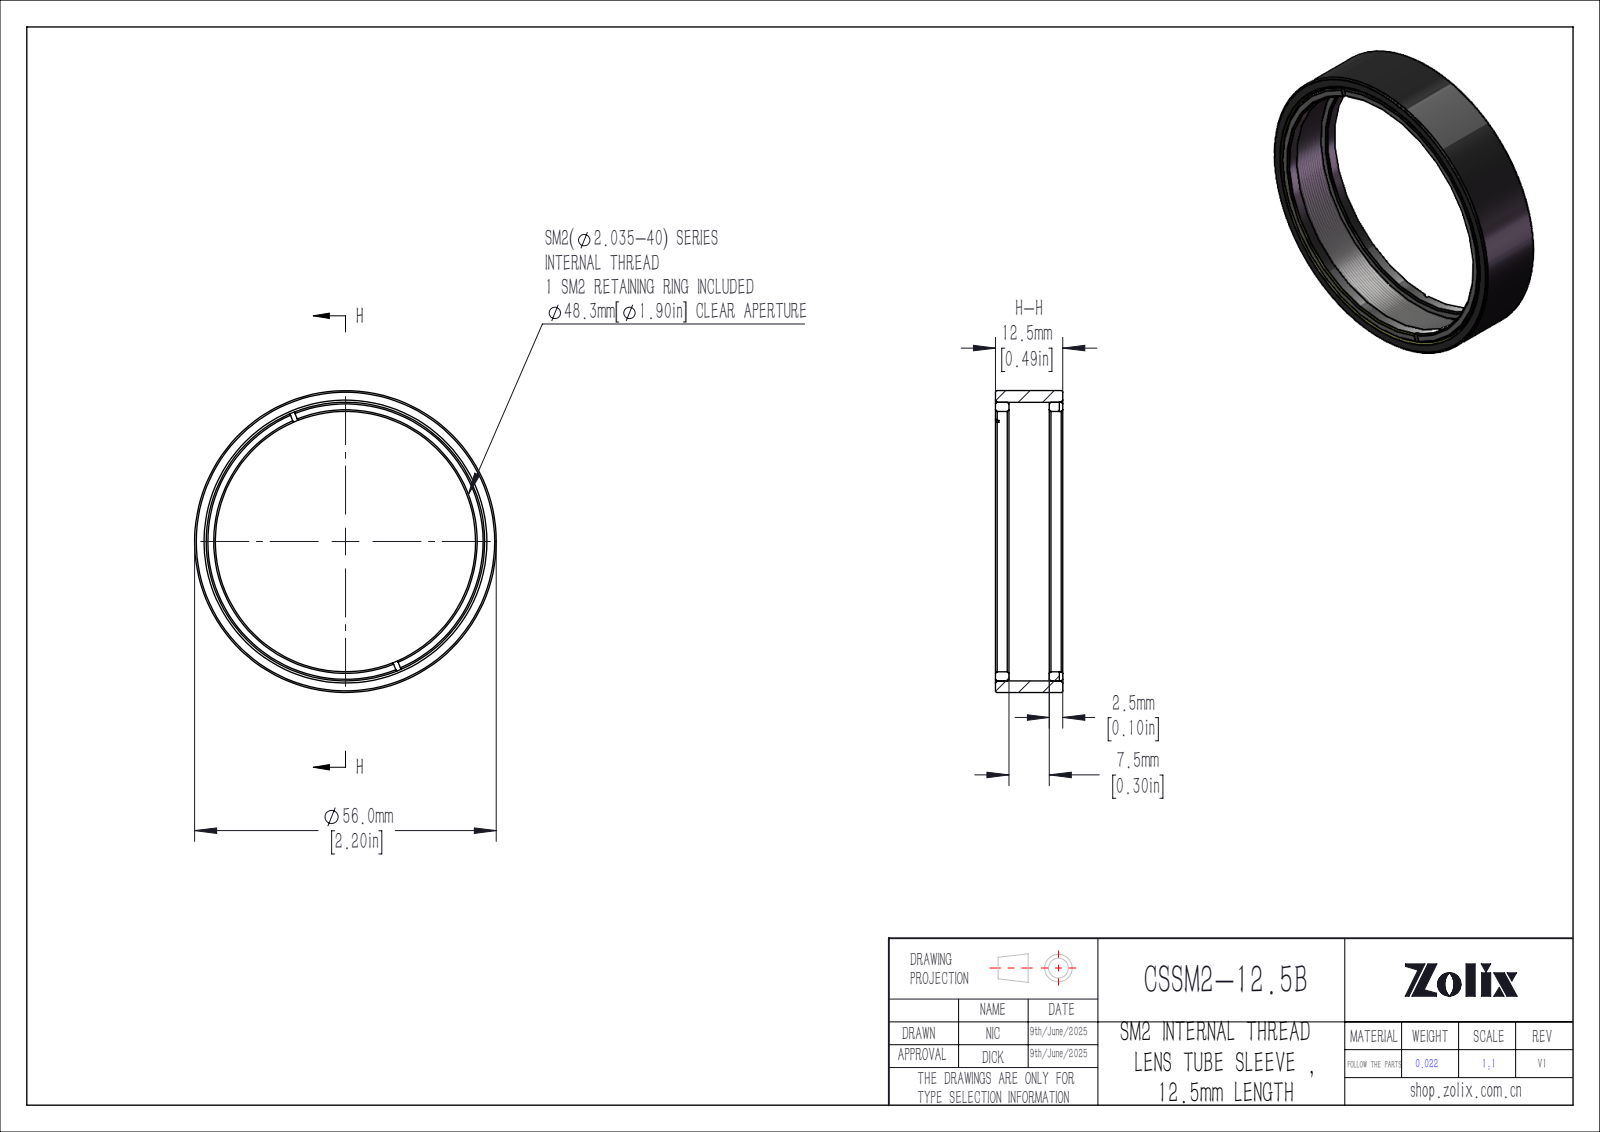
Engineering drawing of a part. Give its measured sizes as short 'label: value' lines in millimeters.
name: CSSM2-12.5B
written by: SolidWorks 2020 (CONFIG_CONTROL_DESIGN)
unit: mm
bodies: 3 solids, 390 faces (74 planar, 35 cylindrical, 281 other)
size: 56 × 56 × 12.5
volume: 5 793 mm³; area: 7 259 mm²
holes: 1× ⌀48.3
bosses: 1× ⌀56, 1× ⌀51.69
rounds: 1× R27.98
face distances: 12.5, 2.5, 10, 7.5, 0.65, 11.85, 1.85, 9.35, 0.9, 11.2
